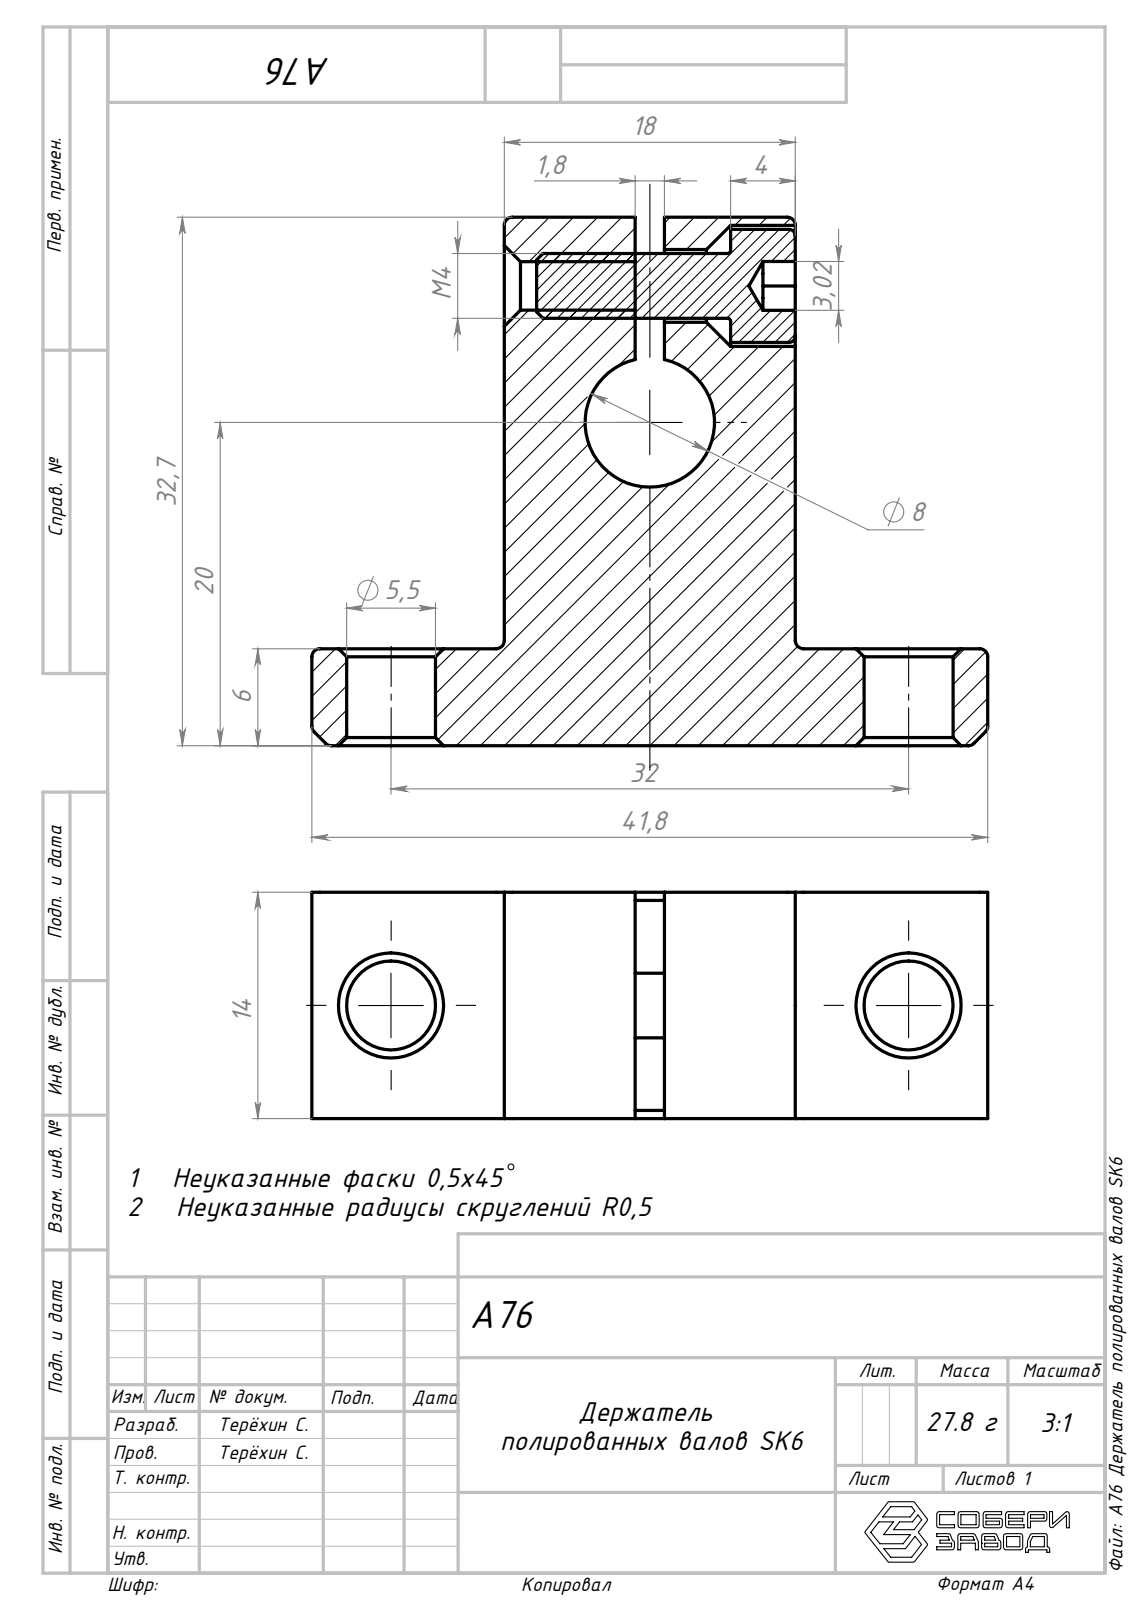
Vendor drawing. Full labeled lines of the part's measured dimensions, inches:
Part name (STEP PRODUCT): socket head cap screw_din_DIN 912 M4 x 12 --- 12N; Сборка2; A76 Держатель полированных валов SK6_00
STEP written by: SolidWorks 2024 (AUTOMOTIVE_DESIGN)
Units: inches
Bodies: 2 solids, 83 faces (30 planar, 27 cylindrical, 26 other)
Overall size (bounding box): 1.646 × 1.287 × 0.551
Volume: 0.547 in³ · Surface area: 6.983 in²
Round holes (diameter × count): ⌀0.217 ×2, ⌀0.118 ×1, ⌀0.177 ×1, ⌀0.295 ×1, ⌀0.315 ×1
Round bosses / shafts (diameter × count): ⌀0.276 ×1, ⌀0.157 ×1
Partial cylindrical surfaces — rounded edges, fillets, slot ends (radius × count): R0.02 ×10
Main face-to-face distances: 0.551, 0.709, 0.236, 0.319, 0.39, 1.287, 1.051, 0.469, 0.787, 0.858
Hole centre spacings: 1.26
